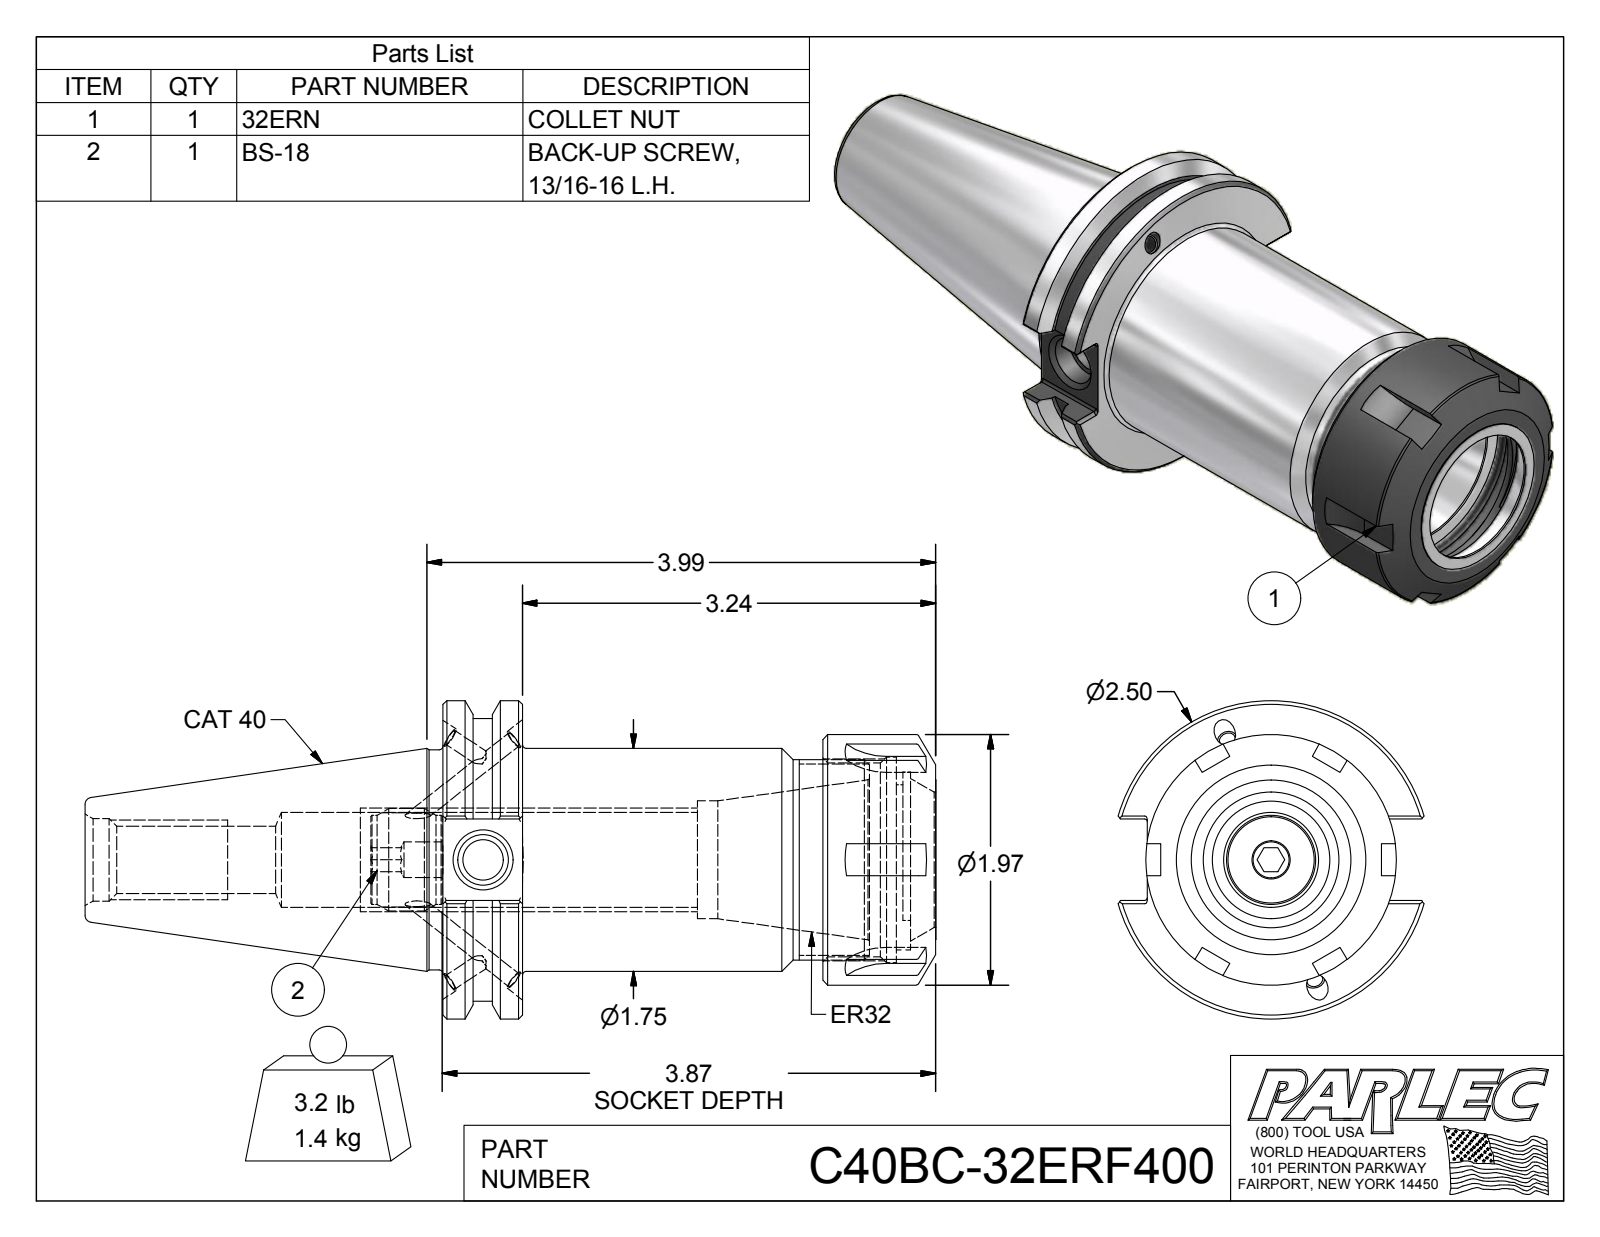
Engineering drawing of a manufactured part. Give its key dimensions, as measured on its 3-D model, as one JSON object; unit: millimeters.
{"part_name": "C40BCB-32ER4-1; 029-965; 32ERN; BS-18 (+1 more)", "step_written_by": "Autodesk Inventor 2016 (AUTOMOTIVE_DESIGN)", "units": "millimeters", "bodies": {"solids": 7, "faces": 263, "planar": 119, "cylindrical": 70, "other": 74}, "overall_size": [169.86, 63.5, 61.05], "volume_mm3": 187530, "surface_area_mm2": 46498, "round_holes": [[3.3, 4], [4.1, 4], [7.11, 1], [8, 1], [10.13, 1], [13.39, 1], [16.46, 1], [18.92, 1], [23.5, 1], [27, 1], [33.02, 1], [38.65, 1]], "round_bosses_or_shafts": [[4.2, 4], [4, 4], [63.5, 1], [56.36, 1], [50, 1], [44.45, 1], [43.94, 1], [40, 1]], "partial_cylinders_radius": [[0.51, 24], [14.9, 1], [17.5, 1]], "face_to_face_distances": [15.87, 98.42, 82.55, 75.64, 59.77, 22.78, 90.65, 74.78, 15.01, 7.77], "hole_center_spacings": [1.86]}
